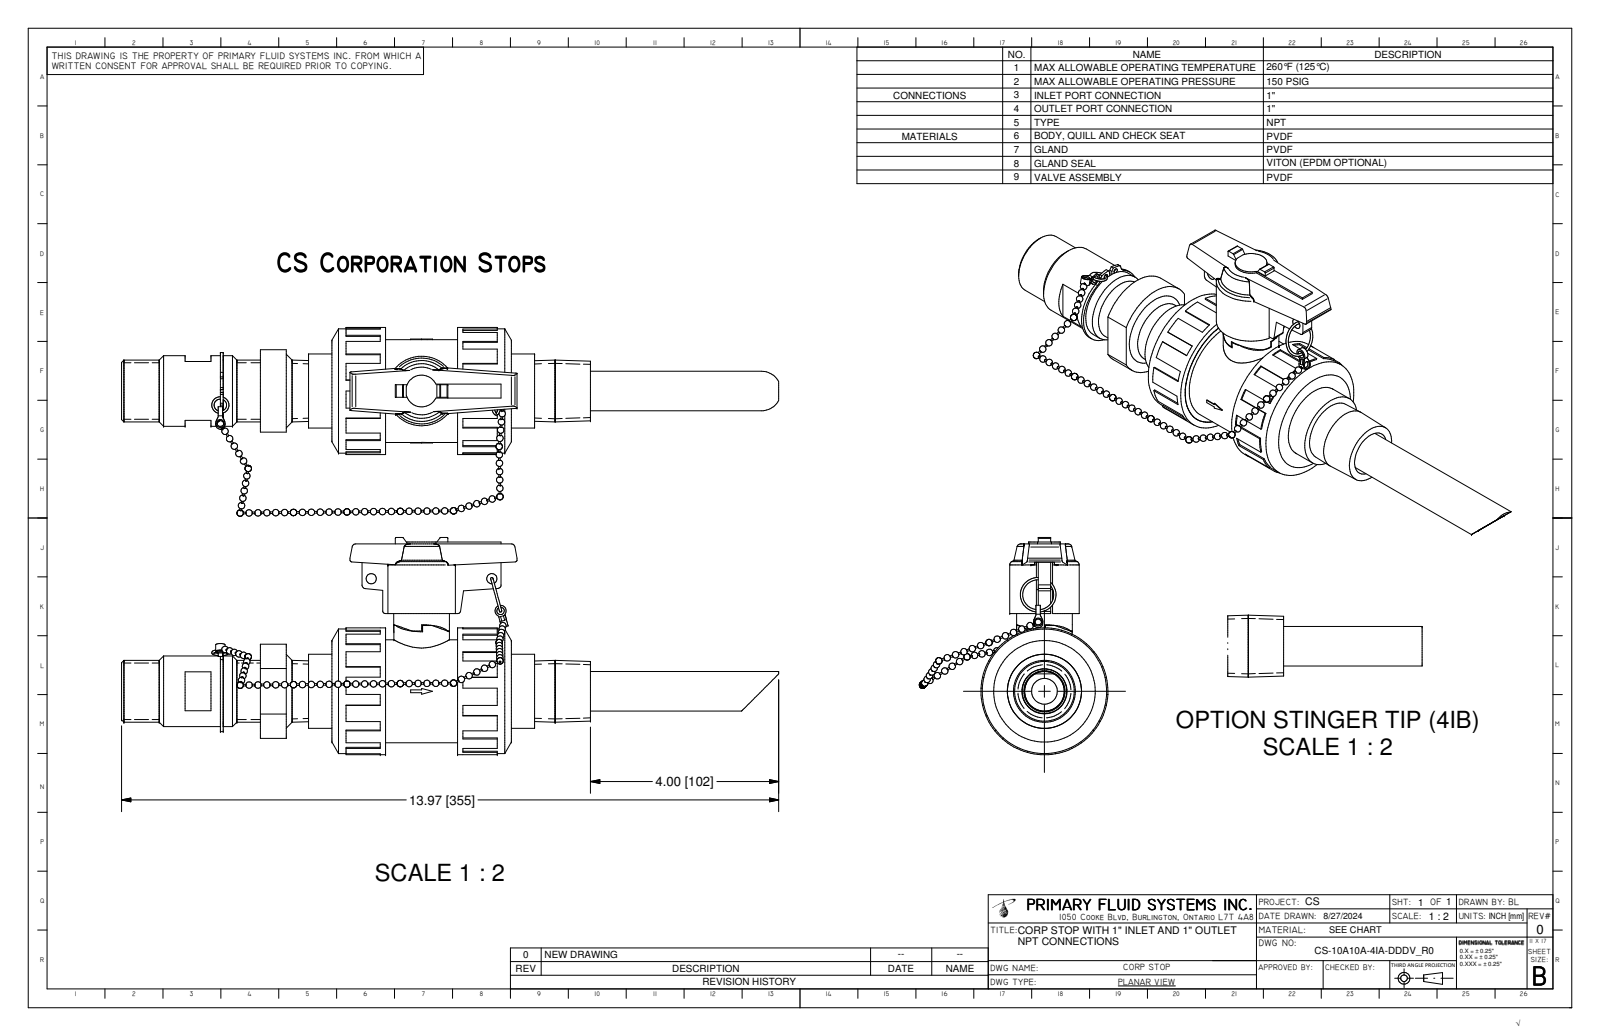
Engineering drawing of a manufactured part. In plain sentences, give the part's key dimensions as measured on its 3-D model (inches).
Its 3-D file was written by "Autodesk Inventor 2025 (CONFIG_CONTROL_DESIGN)". It is 19 solids with 530 faces: 303 planar, 131 cylindrical and 96 other. Overall it measures 13.966 by 4.614 by 4.008 inches. Its volume is 29.1 cubic inches and its surface area 228.8 square inches. Round holes: 2 of diameter 0.098, 2 of diameter 0.15, 2 of diameter 0.157, 2 of diameter 0.217, 1 of diameter 0.546, 1 of diameter 0.875, 1 of diameter 0.957, 1 of diameter 0.984, 1 of diameter 1.26, 1 of diameter 1.306, 1 of diameter 1.386, 1 of diameter 1.575. Round bosses or shafts: 9 of diameter 0.035, 2 of diameter 0.236, 1 of diameter 2.697, 1 of diameter 2.643, 1 of diameter 2.426, 1 of diameter 2.184, 1 of diameter 1.634, 1 of diameter 1.574. Partial cylindrical surfaces (rounded edges, fillets, slot ends): 4 of radius 0.02, 4 of radius 0.079, 2 of radius 0.039, 2 of radius 0.054, 2 of radius 0.059, 2 of radius 0.098, 2 of radius 0.197, 1 of radius 0.337. The main face-to-face distances are 0.907, 2.437, 3.344, 0.906, 2.437, 0.235, 0.235, 1.142, 2.672, 3.579. The hole center spacings are 0.795, 0.295, 0.314, 0.605, 0.708, 0.97, 2.563, 2.832.
